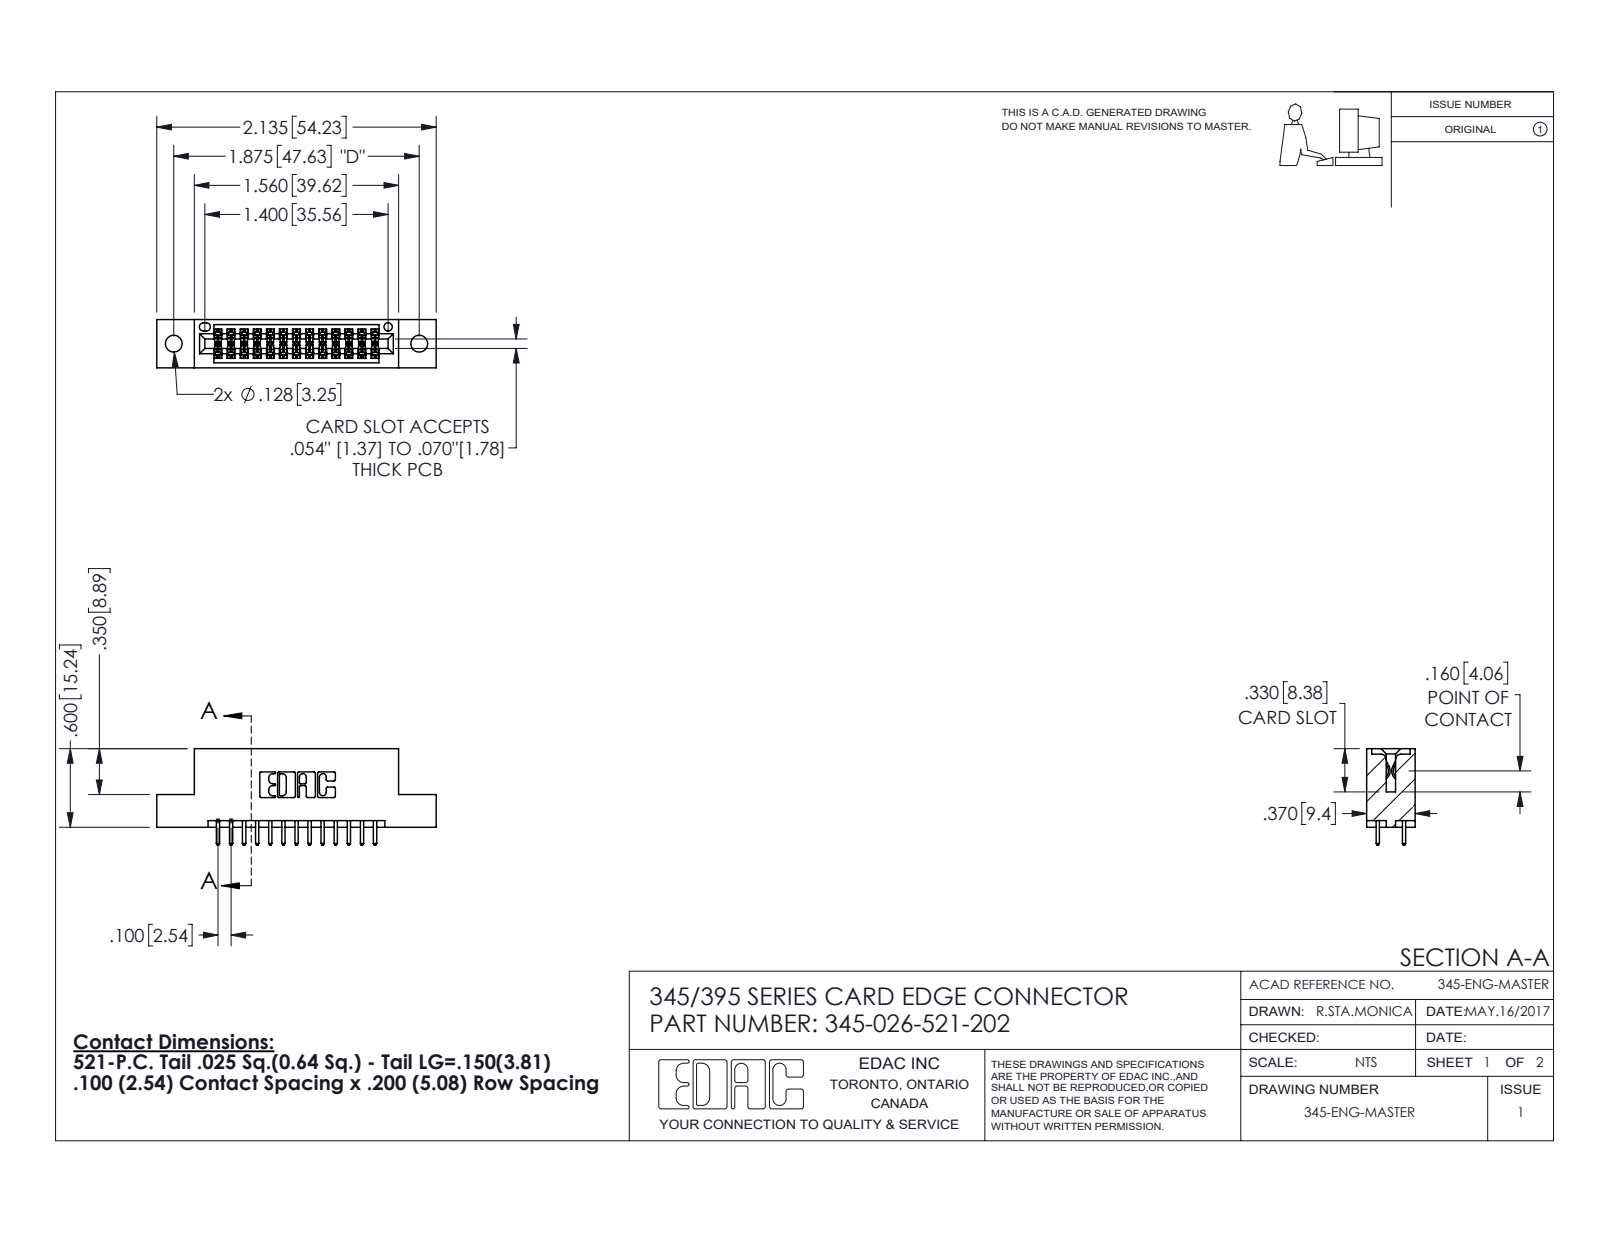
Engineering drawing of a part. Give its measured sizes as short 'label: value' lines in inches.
name: 345-026-521-202; 345-292-001_345-293-121; 345 Part_Flush Mounting Lugs - 0.128 Dia
written by: SolidWorks 2016 (CONFIG_CONTROL_DESIGN)
unit: in
bodies: 27 solids, 1426 faces (938 planar, 488 cylindrical, 0 other)
size: 2.135 × 0.737 × 0.37
volume: 0.302 in³; area: 9.944 in²
holes: 2× ⌀0.128, 1× ⌀0.064
rounds: 39× R0.006, 26× R0.01, 22× R0.01, 6× R0.007, 6× R0.031, 3× R0.026, 2× R0.014, 2× R0.019
face distances: 0.2, 0.298, 0.072, 0.37, 0.098, 0.272, 0.025, 0.225, 0.1, 0.175
hole spacings: 0.27, 1.643, 1.875
